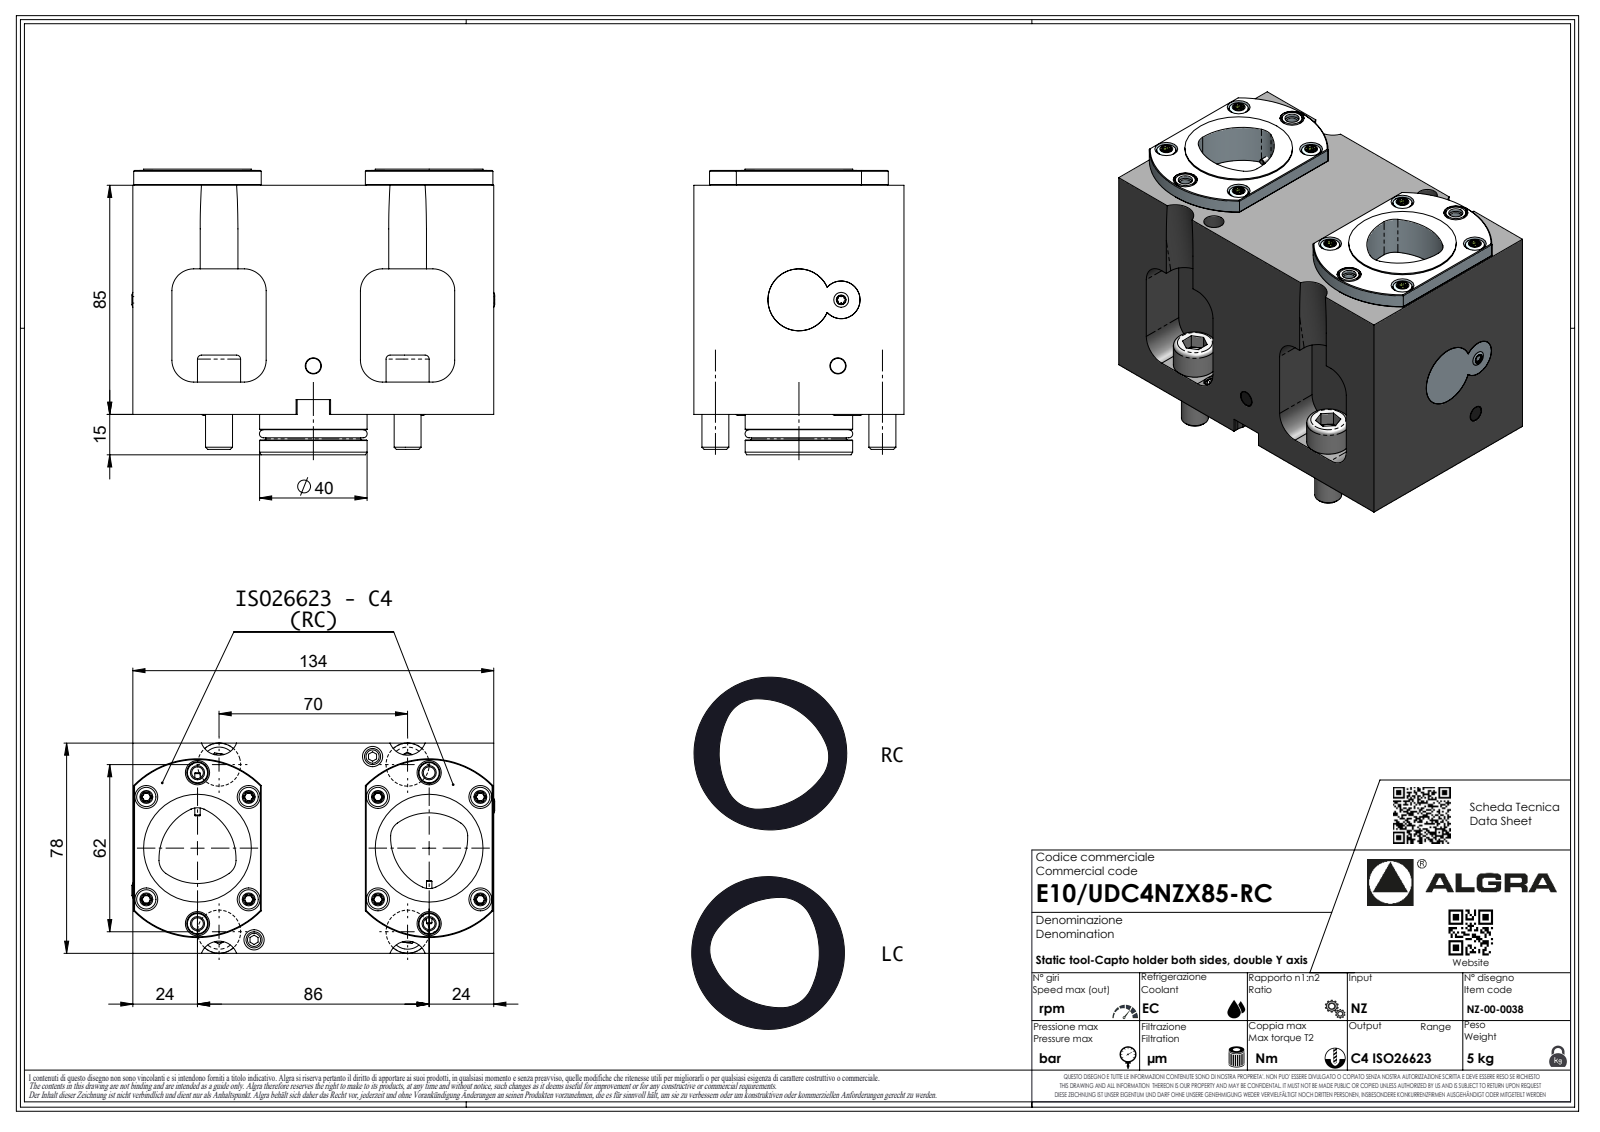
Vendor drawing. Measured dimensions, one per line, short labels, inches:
name: E10UDC4NZX85-RC
written by: SolidWorks 2023 (AUTOMOTIVE_DESIGN)
unit: in
bodies: 1 solid, 799 faces (368 planar, 245 cylindrical, 186 other)
size: 5.276 × 4.173 × 3.071
volume: 50.92 in³; area: 122.1 in²
holes: 4× ⌀0.171, 4× ⌀0.209, 4× ⌀0.315, 4× ⌀0.354, 1× ⌀0.083, 1× ⌀0.236
bosses: 8× ⌀0.281, 4× ⌀0.63, 4× ⌀0.394, 2× ⌀1.575, 1× ⌀1.571, 1× ⌀1.386, 1× ⌀0.251, 1× ⌀0.067
rounds: 48× R0.013, 48× R0.033, 24× R0.197, 8× R0.056, 8× R0.319, 6× R0.013, 6× R0.146, 6× R0.236
face distances: 3.071, 3.346, 5.276, 2.402, 0.669, 0.217, 1.378, 1.732, 3.563, 1.949
hole spacings: 2.205, 3.386, 4.041, 1.487
